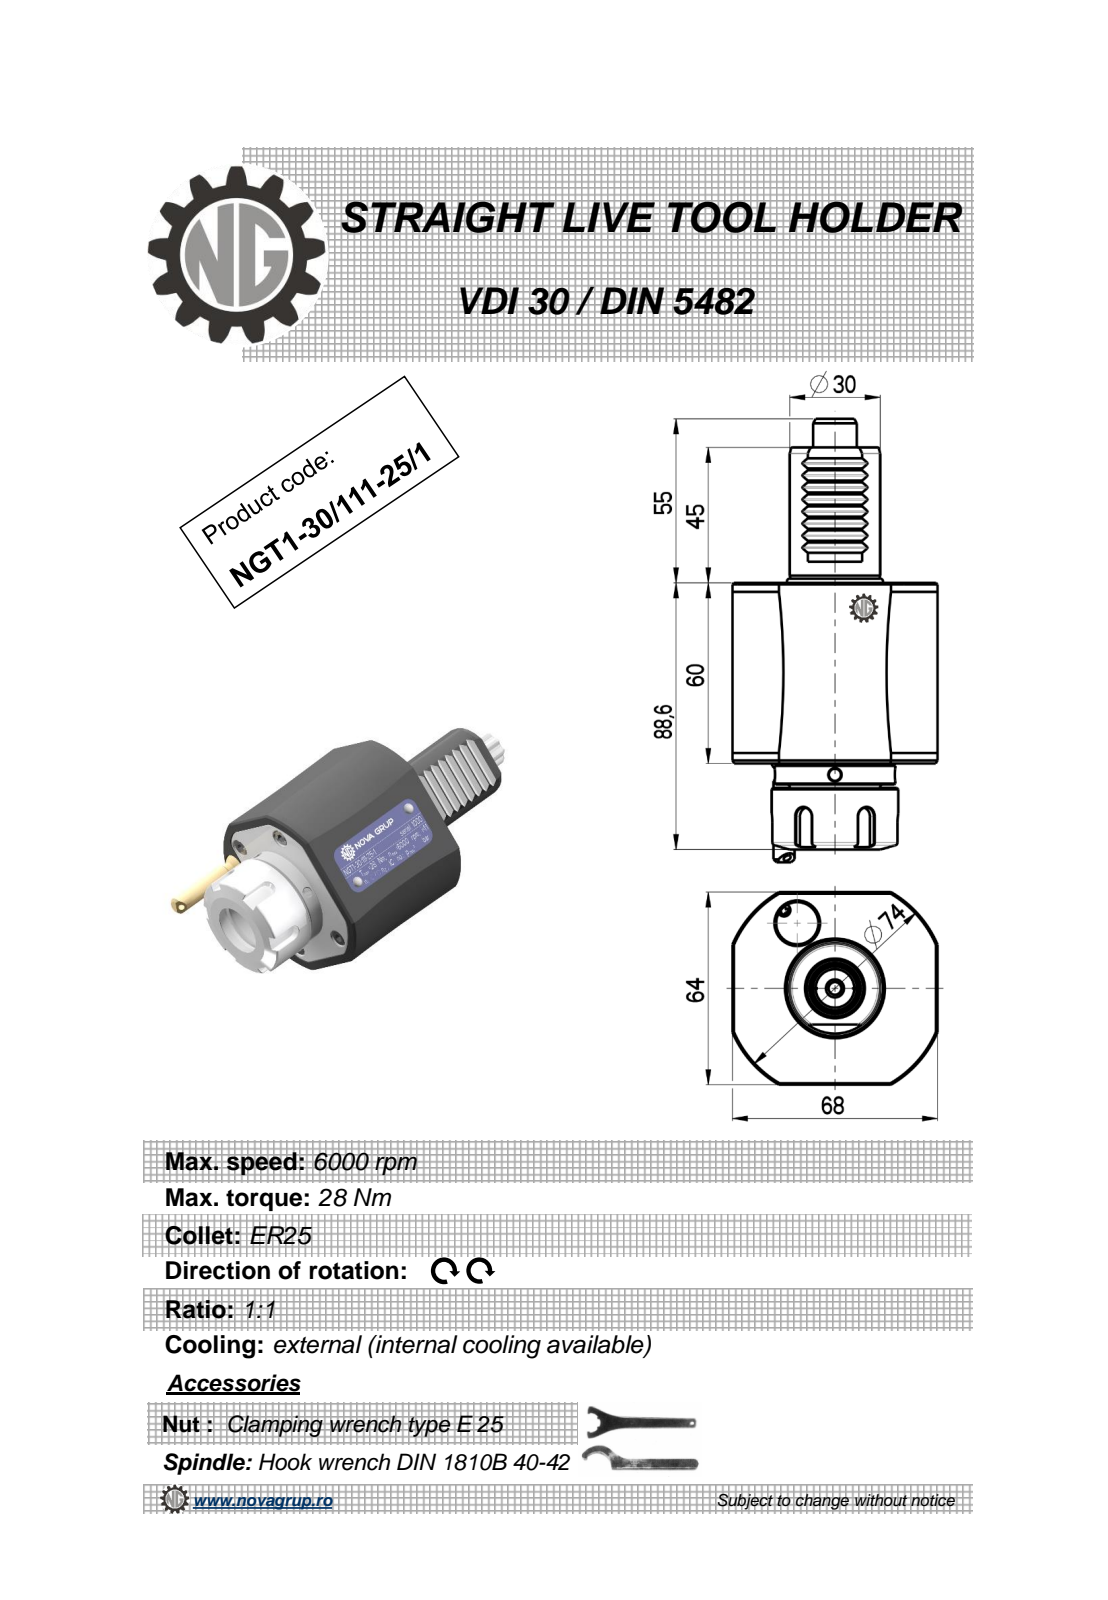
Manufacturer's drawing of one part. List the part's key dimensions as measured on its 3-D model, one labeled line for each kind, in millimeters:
Part name (STEP PRODUCT): NGT1_30_111_25_1
STEP written by: PRO/ENGINEER BY PARAMETRIC TECHNOLOGY CORPORATION, 2010280 (CONFIG_CONTROL_DESIGN)
Units: millimetres
Bodies: 1 solid, 290 faces (89 planar, 94 cylindrical, 107 other)
Overall size (bounding box): 147.83 × 68 × 65.6
Volume: 298 239 mm³ · Surface area: 34 101 mm²
Round holes (diameter × count): ⌀4 ×2, ⌀2.5 ×1, ⌀3 ×1, ⌀4.2 ×1, ⌀20.3 ×1, ⌀25.8 ×1
Round bosses / shafts (diameter × count): ⌀42 ×1, ⌀40 ×1, ⌀33 ×1, ⌀30 ×1, ⌀9 ×1, ⌀7 ×1, ⌀5 ×1
Partial cylindrical surfaces — rounded edges, fillets, slot ends (radius × count): R2.91 ×16, R0.3 ×8, R3 ×5, R5.7 ×1, R7.25 ×1, R13.9 ×1, R37 ×1
Main face-to-face distances: 60, 64, 68, 81.7, 21.7, 2.83, 45, 105, 126.7, 113.1
Hole centre spacings: 1.5, 29.75, 31
